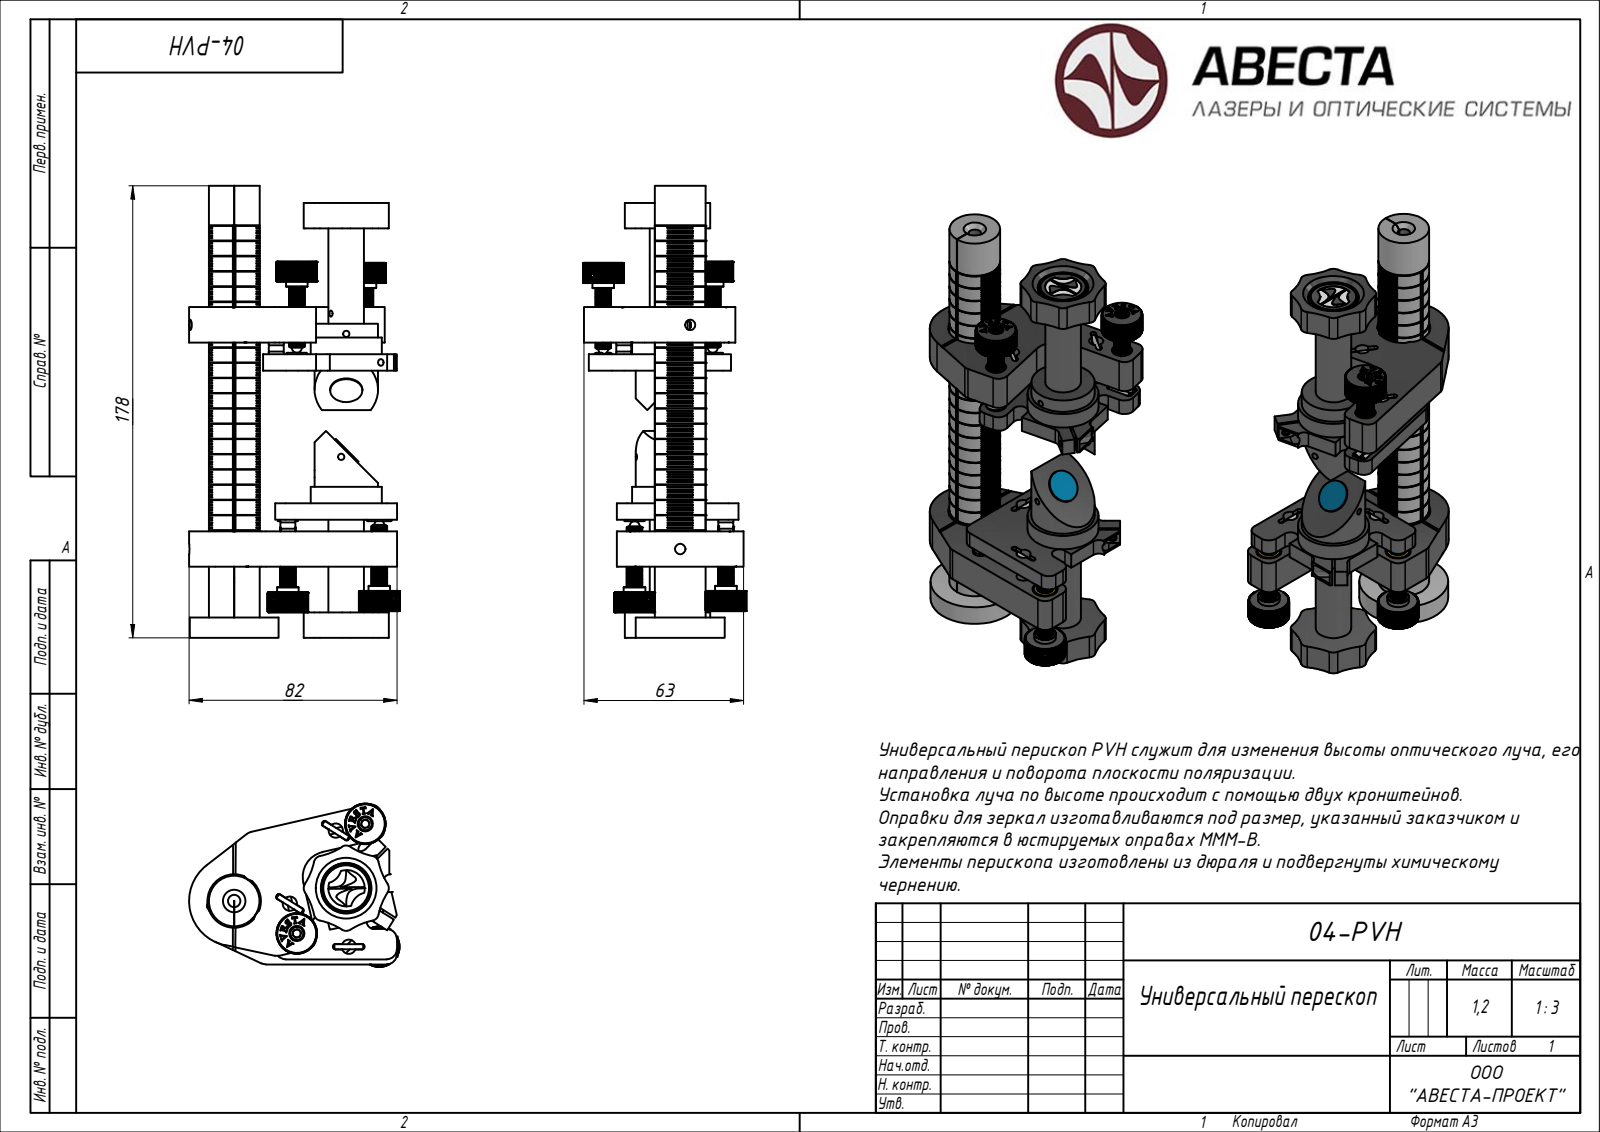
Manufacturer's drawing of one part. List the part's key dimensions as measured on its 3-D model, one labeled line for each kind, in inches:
Part name (STEP PRODUCT): Block 01; Block 03; Block 04; Block 05
STEP written by: ST-DEVELOPER v15 (AUTOMOTIVE_DESIGN)
Units: inches
Bodies: 4 solids, 4079 faces (0 planar, 0 cylindrical, 4079 other)
Overall size (bounding box): 6.74 × 3.263 × 2.532
